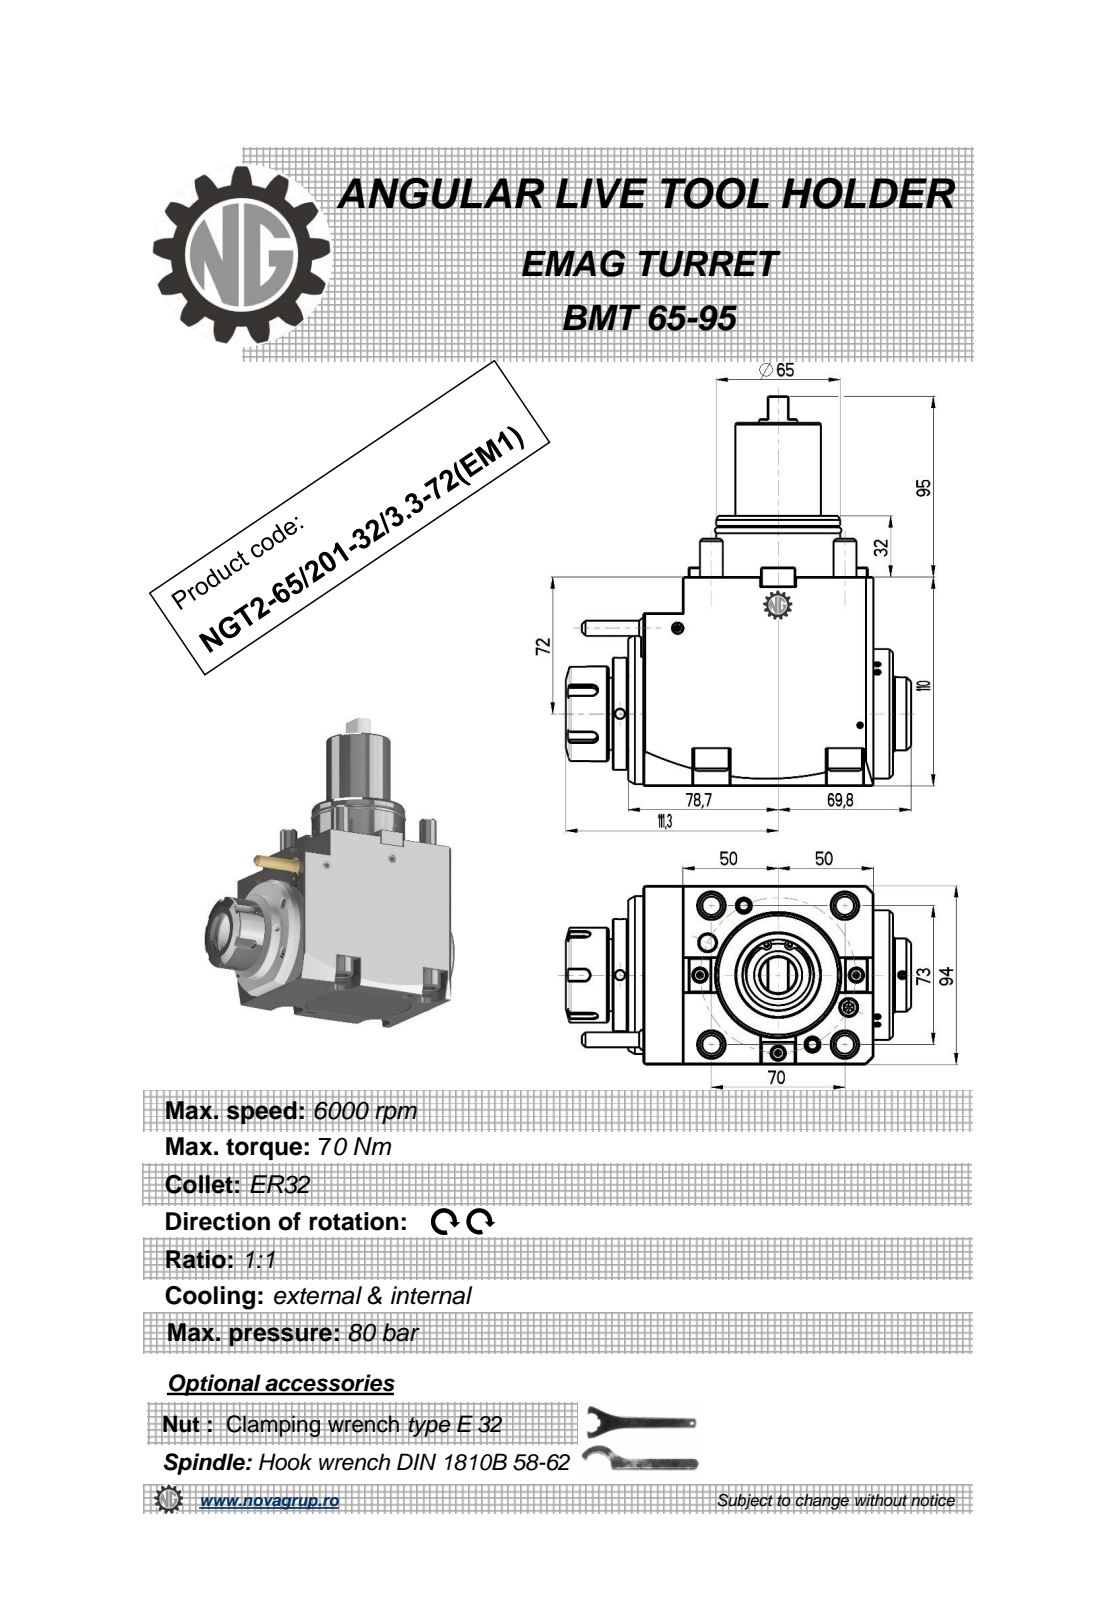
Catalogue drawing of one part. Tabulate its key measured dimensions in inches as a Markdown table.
| quantity | value |
| --- | --- |
| part name | NGT2_65_201_32_3_3_72_EM1 |
| STEP written by | PRO/ENGINEER BY PARAMETRIC TECHNOLOGY CORPORATION, 2010280 (CONFIG_CONTROL_DESIGN) |
| units | inches |
| bodies | 2 solids, 445 faces (217 planar, 112 cylindrical, 116 other) |
| overall size | 8.071 × 7.13 × 3.701 |
| volume | 93.92 in³ |
| surface area | 171.4 in² |
| round holes (diameter × count) | 0.197 × 3, 0.335 × 2, 0.118 × 1, 1.063 × 1 |
| round bosses / shafts (diameter × count) | 0.709 × 4, 0.472 × 4, 3.268 × 1, 2.677 × 1, 2.559 × 1, 2.362 × 1, 2.323 × 1, 1.969 × 1 |
| partial cylindrical surfaces (radius × count) | 0.014 × 20, 0.009 × 6, 0.118 × 5, 0.374 × 4, 0.031 × 2, 21.654 × 2 |
| main face-to-face distances | 3.701, 4.331, 0.315, 5.067, 3.937, 0.748, 4.752, 5.157, 3.583, 2.008 |
| hole center spacings | 1.929, 2.22, 3.206, 4.77 |
